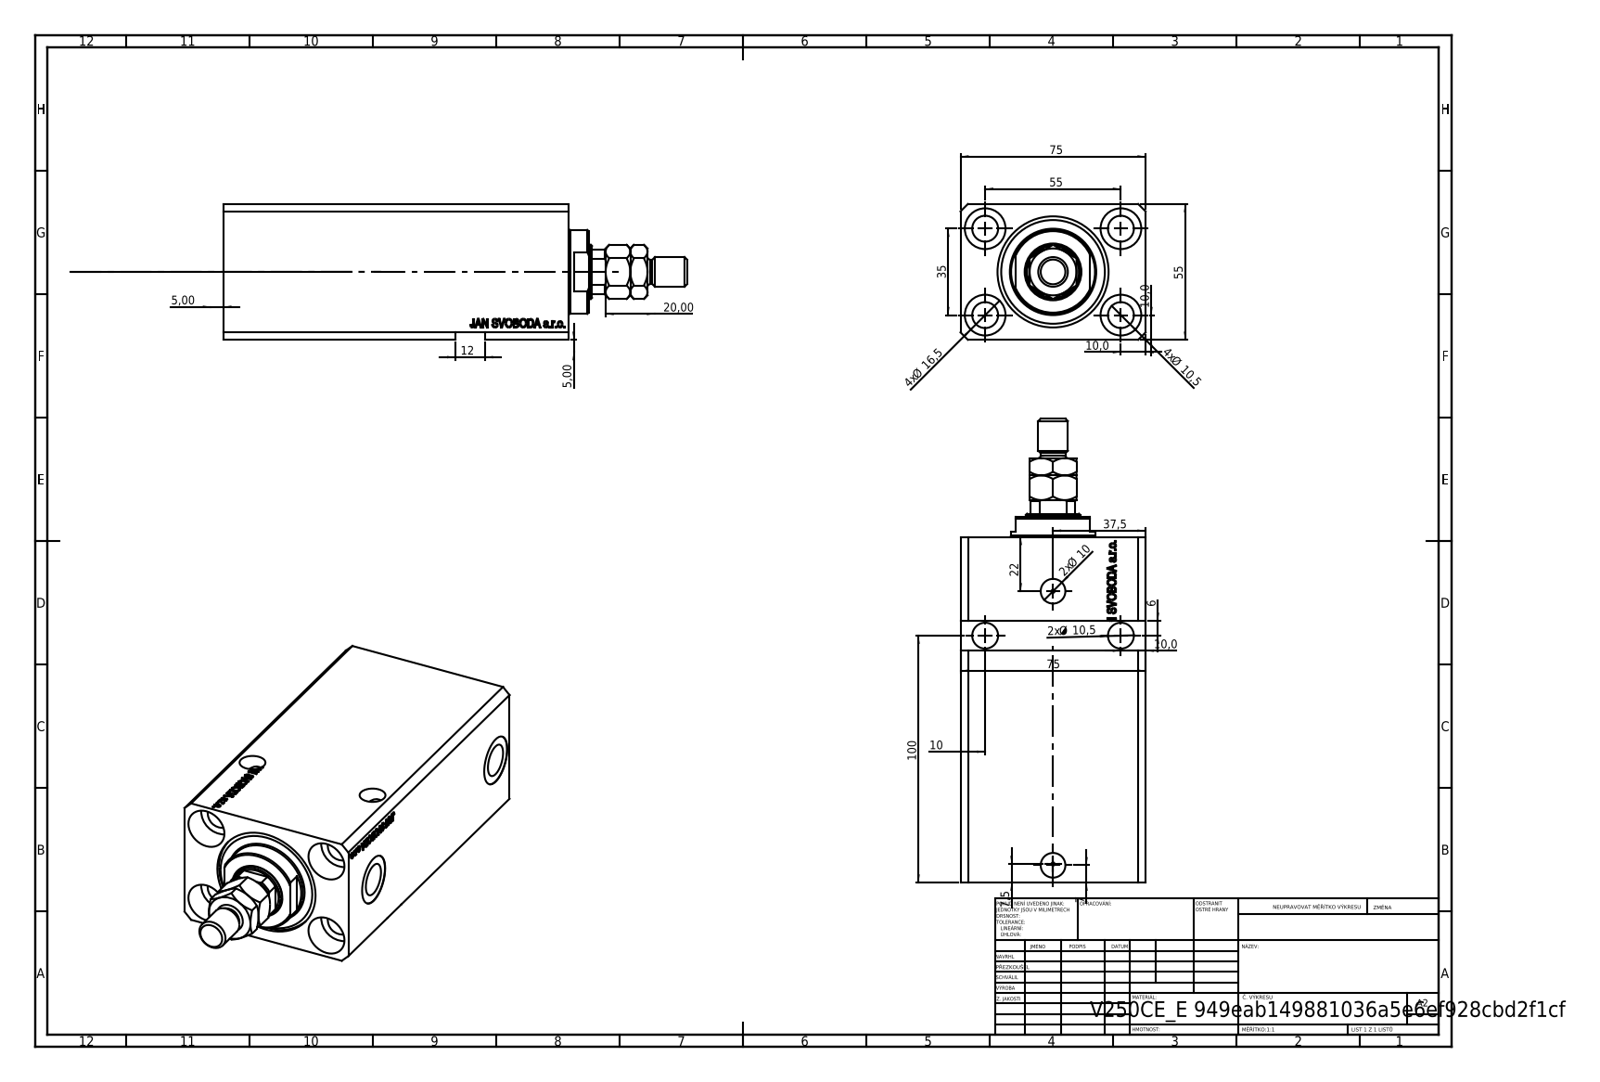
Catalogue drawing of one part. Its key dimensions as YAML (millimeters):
part_name: "V250CE_VC_E; V250CE_C_VCP; V250CE_E_Body; MTA"
step_written_by: "SolidWorks 2019 (CONFIG_CONTROL_DESIGN)"
units: millimeters
bodies: {solids: 4, faces: 943, planar: 453, cylindrical: 88, other: 402}
overall_size: [187.9, 75, 55]
volume: 482600
surface_area: 105429
round_holes:
  - {diameter: 10.5, count: 7}
  - {diameter: 1.25, count: 4}
  - {diameter: 16.5, count: 4}
  - {diameter: 10, count: 2}
  - {diameter: 13.16, count: 2}
  - {diameter: 20, count: 2}
  - {diameter: 22, count: 1}
  - {diameter: 32, count: 1}
  - {diameter: 45, count: 1}
round_bosses_or_shafts:
  - {diameter: 34, count: 1}
  - {diameter: 12, count: 1}
  - {diameter: 10, count: 1}
partial_cylinders:
  - {radius: 10.5, count: 1}
face_to_face_distances: [55, 75, 140, 112.9, 27.1, 9.9, 103, 130.1, 11, 129]
hole_center_spacings: [32.6, 55, 32.87, 35, 65.19, 96.47, 96.98, 0.53]
